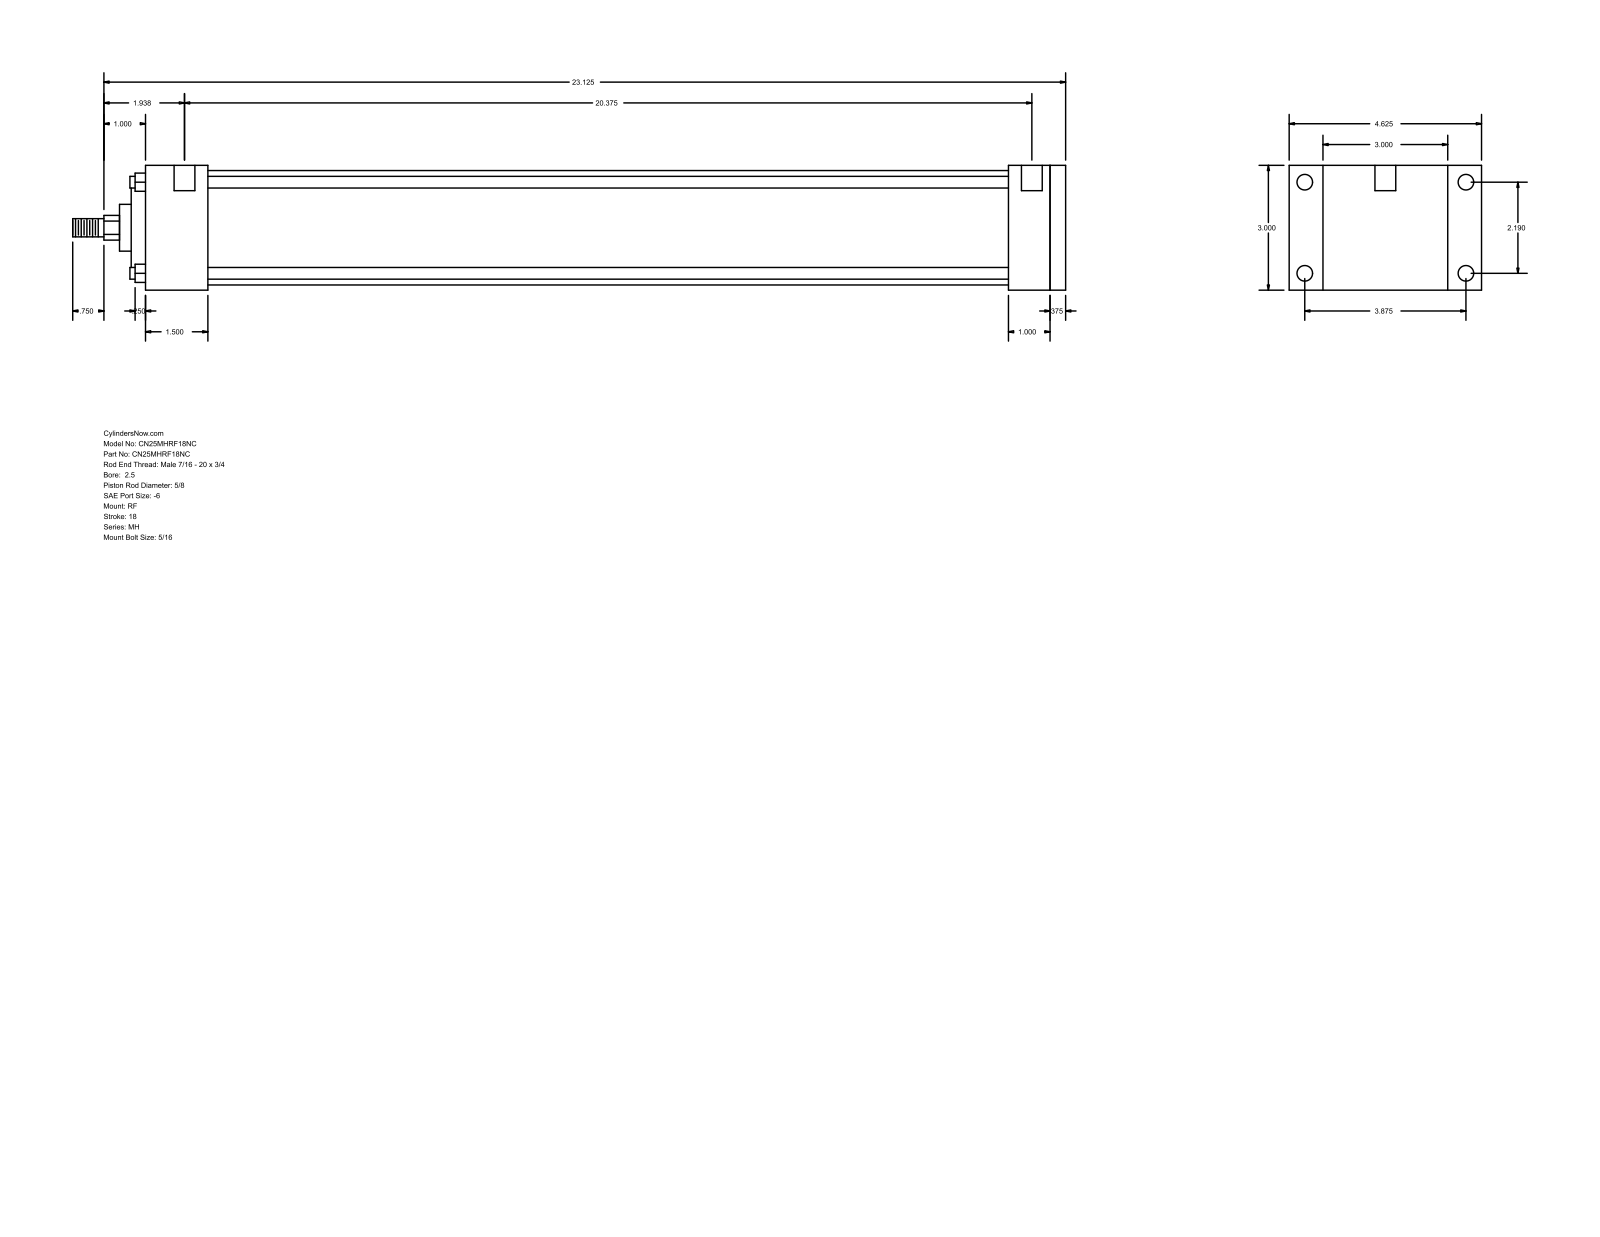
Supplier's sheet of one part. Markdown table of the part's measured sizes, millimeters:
| quantity | value |
| --- | --- |
| part name | MH_RF__0250_0.625 |
| STEP written by | GSSL Pune (CONFIG_CONTROL_DESIGN) |
| units | millimeters |
| bodies | 0 solids, 94 faces (65 planar, 29 cylindrical, 0 other) |
| overall size | 606.42 × 117.47 × 76.2 |
| round holes (diameter × count) | 5.56 × 4, 9.53 × 4, 12.7 × 2 |
| round bosses / shafts (diameter × count) | 7.14 × 4, 69.85 × 1, 55.55 × 1, 28.57 × 1, 15.88 × 1, 11.11 × 1 |
| partial cylindrical surfaces (radius × count) | 7.54 × 1 |
| main face-to-face distances | 76.2, 9.53, 561.98, 552.45, 25.4, 34.93, 38.1, 527.05, 488.95, 514.35 |
| hole center spacings | 55.62, 98.42, 113.05, 525.46, 3.17, 4.76, 517.53, 520.7 |
